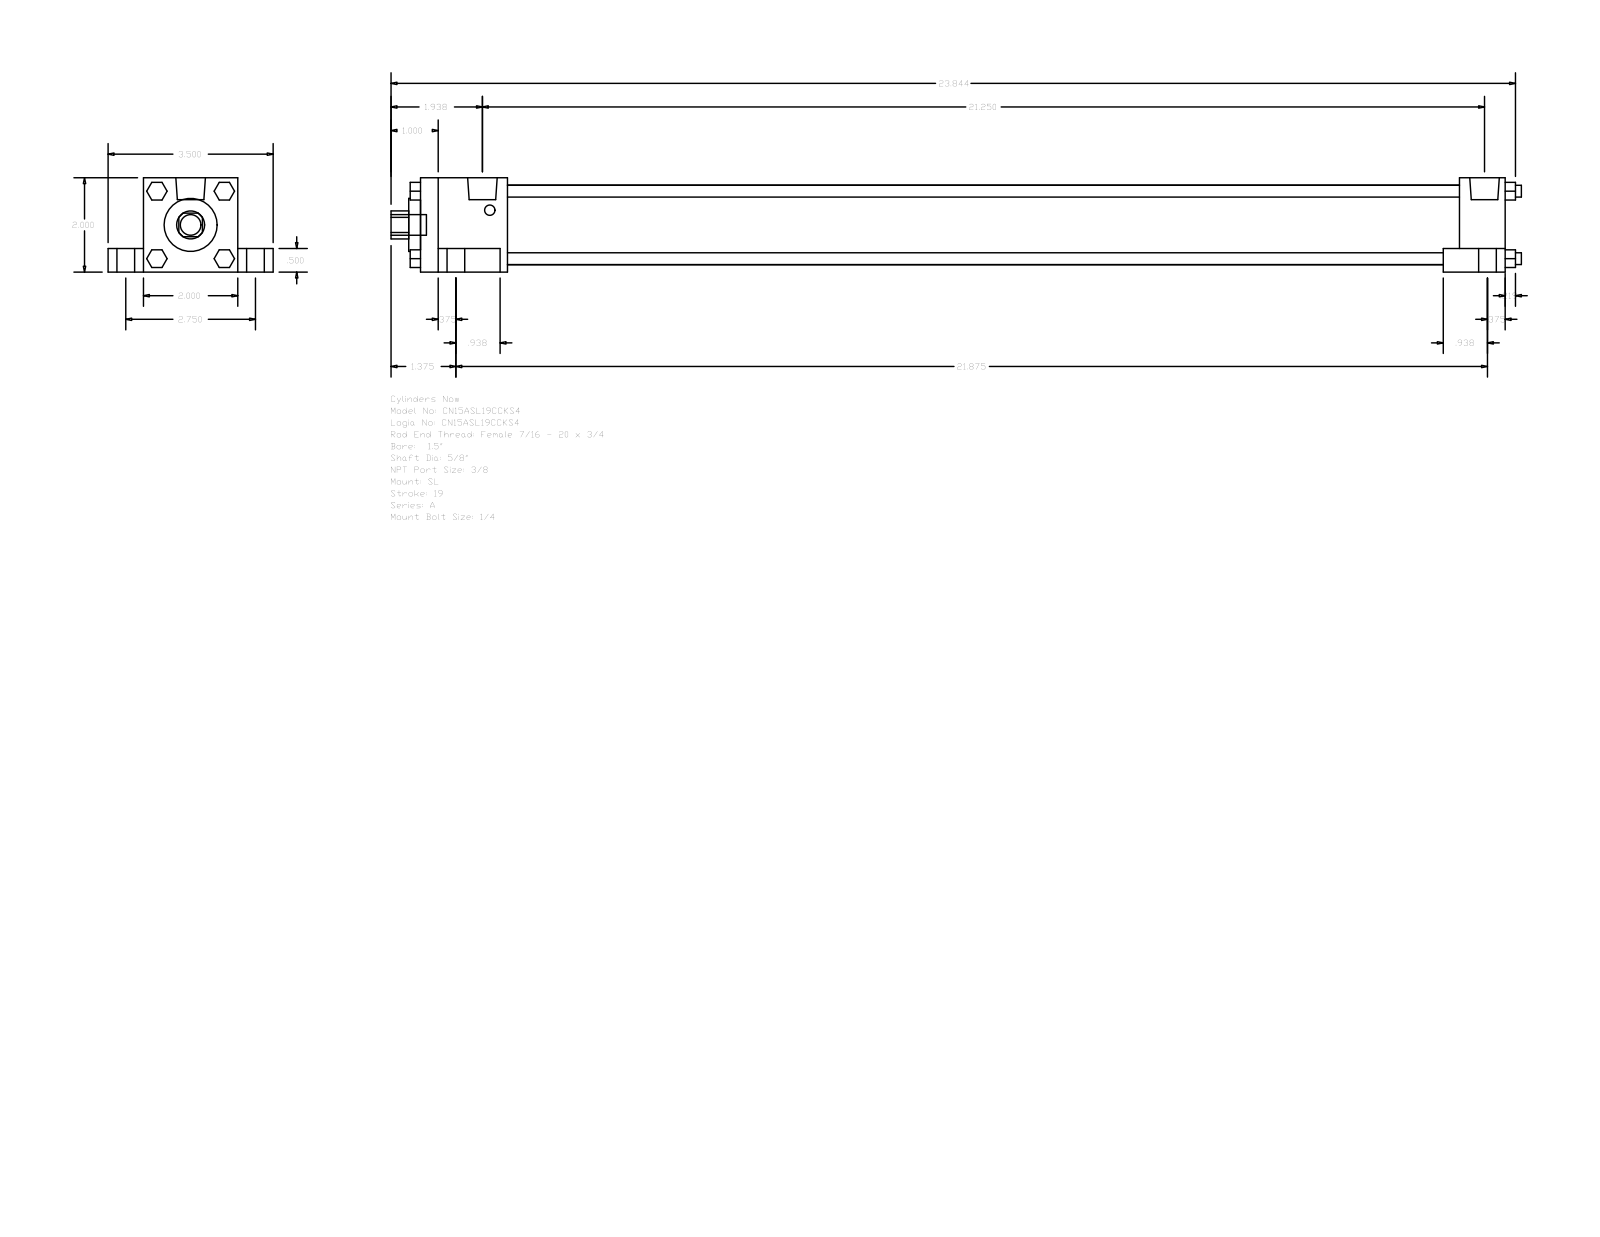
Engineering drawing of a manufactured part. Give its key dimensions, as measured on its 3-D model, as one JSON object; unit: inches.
{"part_name": "A_SL__0150_0.625", "step_written_by": "GSSL Pune (CONFIG_CONTROL_DESIGN)", "units": "inches", "bodies": {"solids": 0, "faces": 148, "planar": 112, "cylindrical": 36, "other": 0}, "overall_size": [23.969, 3.5, 2], "round_holes": [[0.625, 1], [1.125, 1], [1.69, 1]], "round_bosses_or_shafts": [[0.625, 4], [0.375, 4], [0.25, 4], [0.219, 4], [0.627, 2], [0.437, 1]], "partial_cylinders_radius": [[0.297, 1]], "face_to_face_distances": [2, 0.75, 0.5, 1.5, 2.75, 23, 0.375, 1.313, 22.031, 0.969]}
